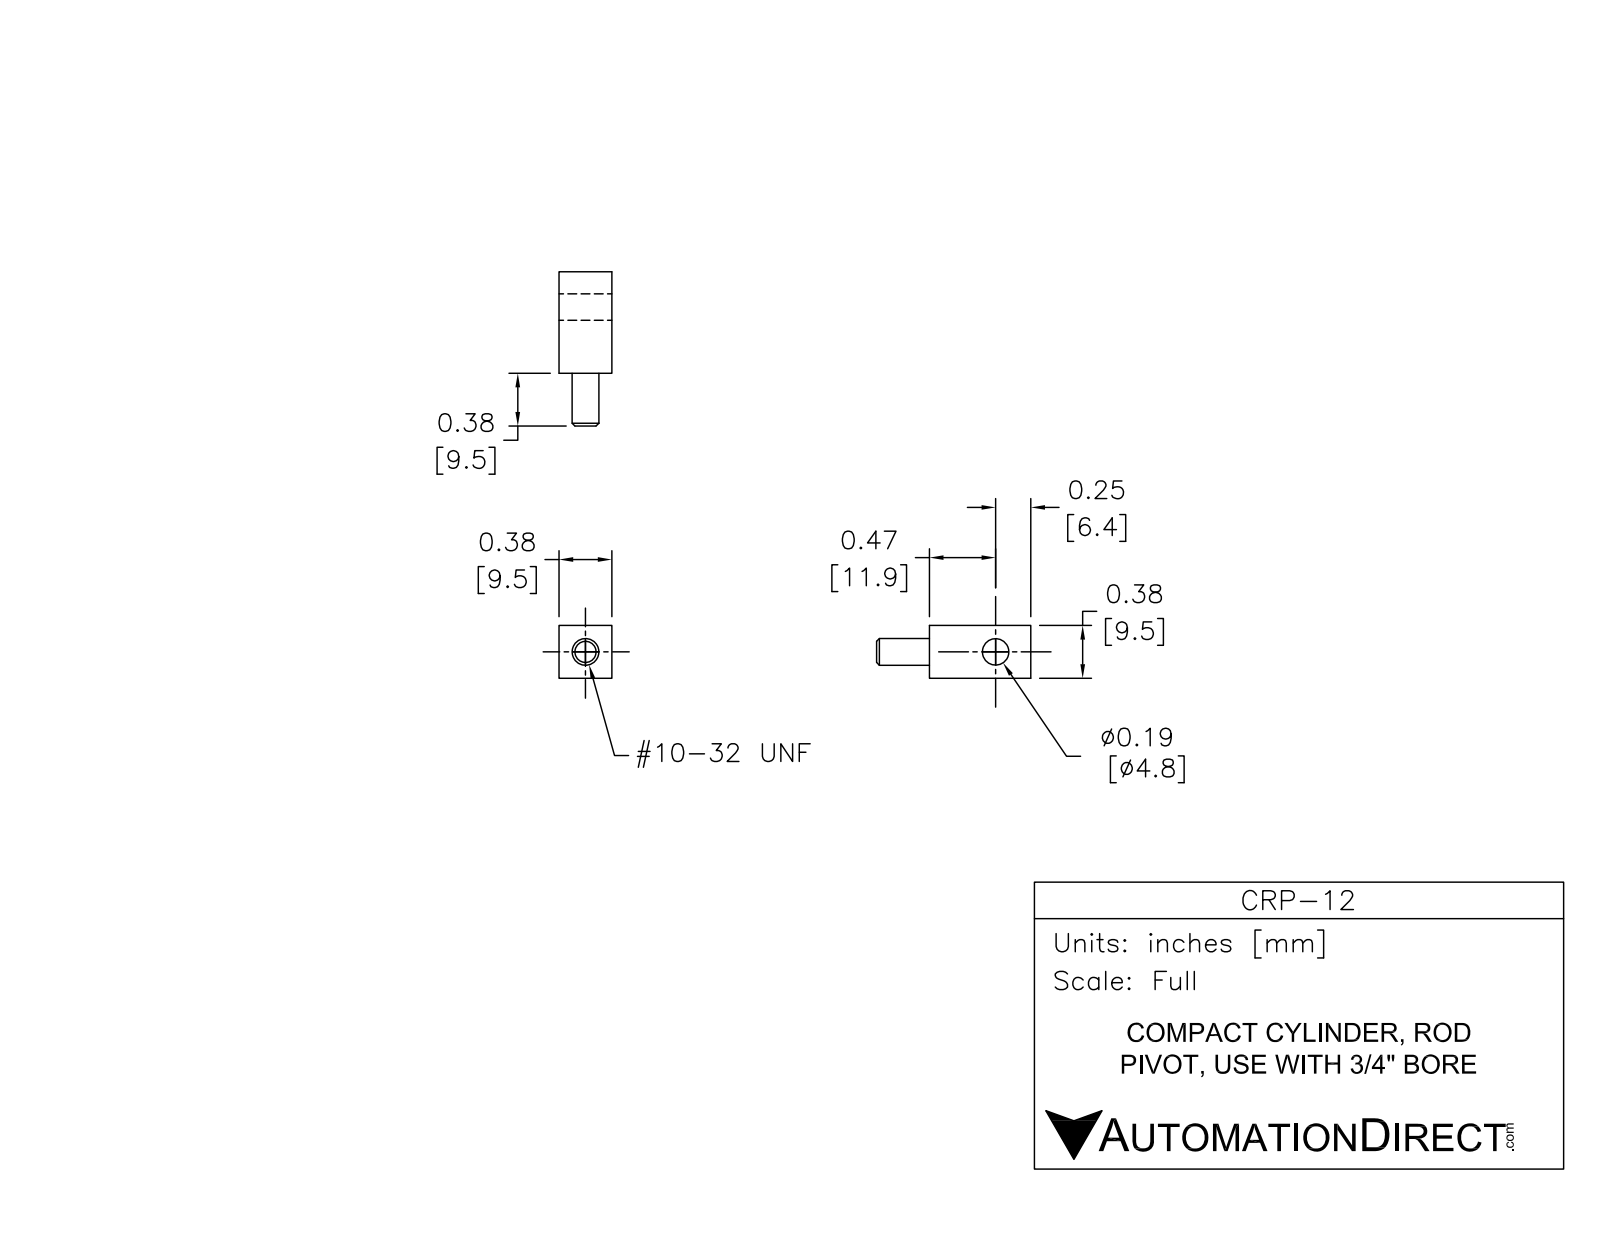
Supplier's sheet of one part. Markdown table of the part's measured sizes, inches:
| quantity | value |
| --- | --- |
| part name | CRP-12_bracket; CRP-12_nut; CRP-12_bushing; CRP-12 |
| STEP written by | SolidWorks 2014 (AUTOMOTIVE_DESIGN) |
| units | inches |
| bodies | 3 solids, 45 faces (17 planar, 10 cylindrical, 18 other) |
| overall size | 1.1 × 0.433 × 0.38 |
| volume | 0.116 in³ |
| surface area | 2.777 in² |
| round holes (diameter × count) | 0.156 × 1, 0.19 × 1, 0.252 × 1 |
| round bosses / shafts (diameter × count) | 0.19 × 1 |
| main face-to-face distances | 0.38, 0.72, 0.12, 0.84, 0.375, 0.378, 0.26, 0.38, 1.1 |
